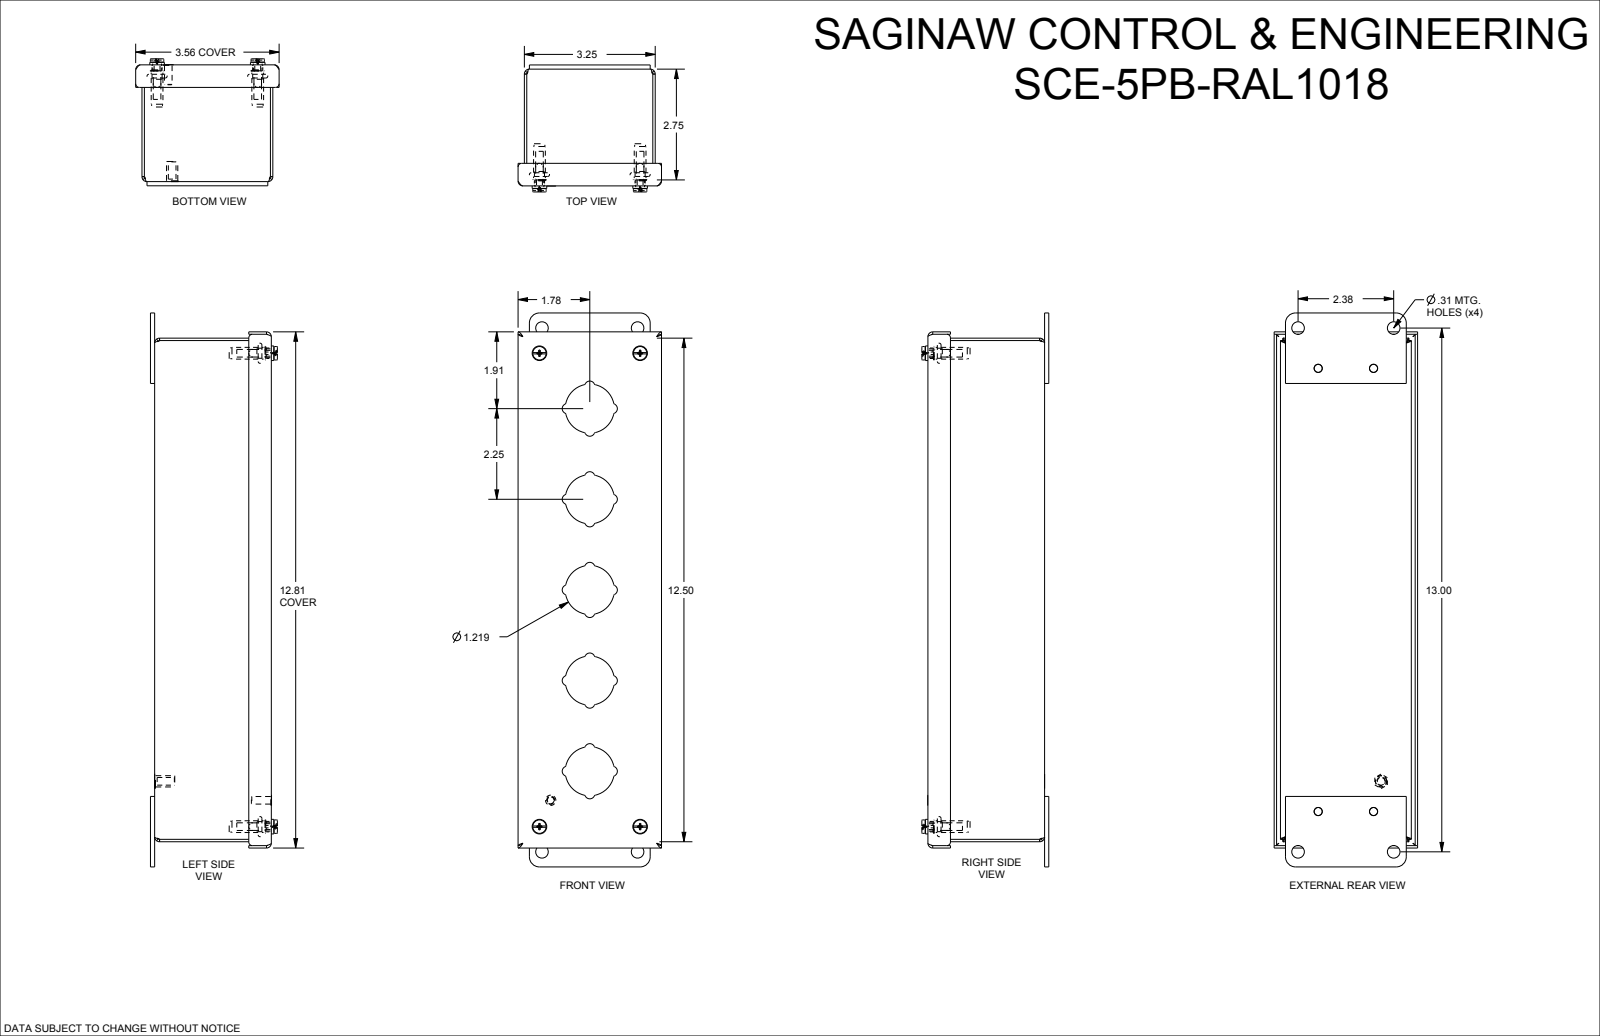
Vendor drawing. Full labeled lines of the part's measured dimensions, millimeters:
Part name (STEP PRODUCT): SCE-5PB-RAL1018
STEP written by: SolidWorks 2021 (AUTOMOTIVE_DESIGN)
Units: millimetres
Bodies: 19 solids, 587 faces (201 planar, 224 cylindrical, 162 other)
Overall size (bounding box): 349.3 × 90.4 × 80.1
Volume: 216 300 mm³ · Surface area: 279 000 mm²
Round holes (diameter × count): ⌀4.8 ×5, ⌀5.2 ×4, ⌀5.6 ×4, ⌀6.4 ×4, ⌀6.4 ×4, ⌀8 ×4, ⌀8.1 ×4
Round bosses / shafts (diameter × count): ⌀4.8 ×5, ⌀11.1 ×4, ⌀9.2 ×4, ⌀8.6 ×4, ⌀8.5 ×4, ⌀7.4 ×4, ⌀6.9 ×4, ⌀6.6 ×4
Partial cylindrical surfaces — rounded edges, fillets, slot ends (radius × count): R1 ×40, R3.2 ×20, R1.5 ×12, R0.5 ×8, R1.6 ×8, R2.7 ×8, R5.8 ×8, R15.5 ×5
Main face-to-face distances: 1.5, 72.1, 81, 70.6, 73.6, 82.6, 79.5, 68.3, 3.8, 316
Hole centre spacings: 298.5, 305.1, 305.1, 16, 63.5, 289.3, 298.4, 314.3
